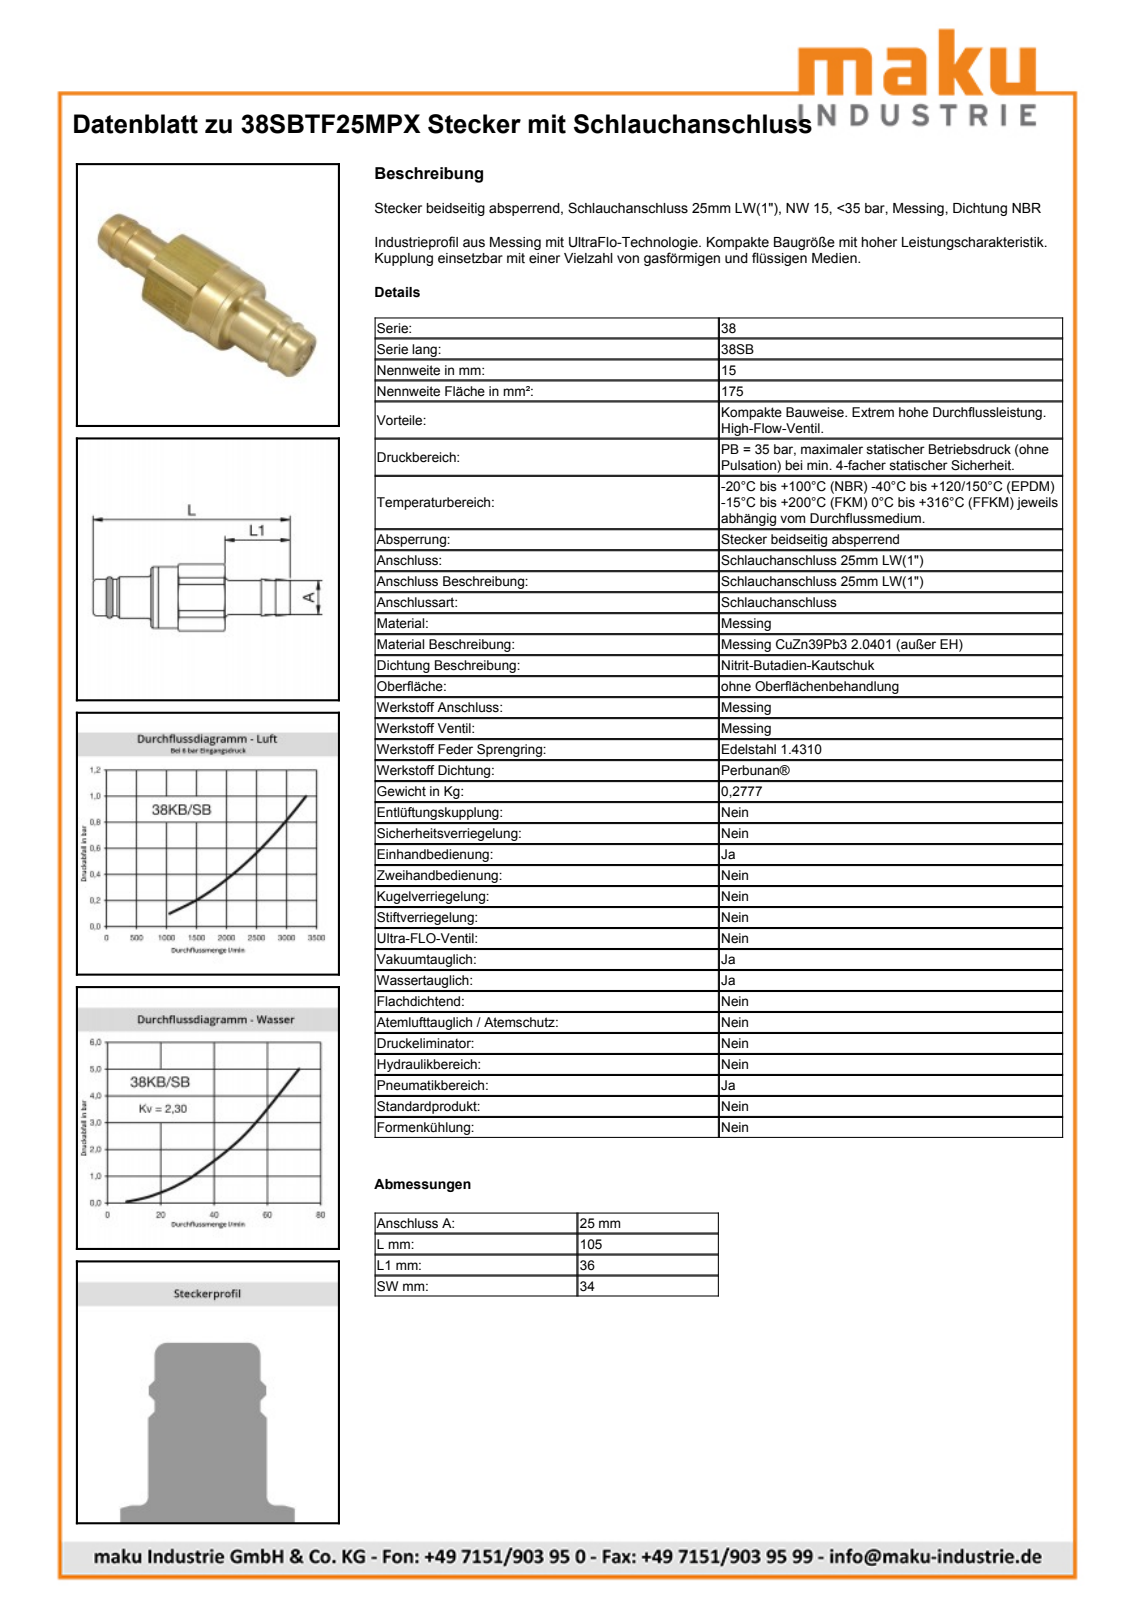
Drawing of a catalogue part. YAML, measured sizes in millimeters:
part_name: "D107817"
step_written_by: "Autodesk Inventor 2013 (AUTOMOTIVE_DESIGN)"
units: millimeters
bodies: {solids: 1, faces: 53, planar: 13, cylindrical: 15, other: 25}
overall_size: [105, 37, 35.5]
volume: 66085
surface_area: 11458
round_holes:
  - {diameter: 12, count: 1}
  - {diameter: 28.95, count: 1}
round_bosses_or_shafts:
  - {diameter: 34, count: 1}
  - {diameter: 28.5, count: 1}
  - {diameter: 25, count: 1}
  - {diameter: 22.85, count: 1}
  - {diameter: 22.6, count: 1}
  - {diameter: 20.3, count: 1}
partial_cylinders:
  - {radius: 18.5, count: 1}
face_to_face_distances: [34, 72.9, 105, 32.1, 36, 69, 36.9, 8, 16, 20]
